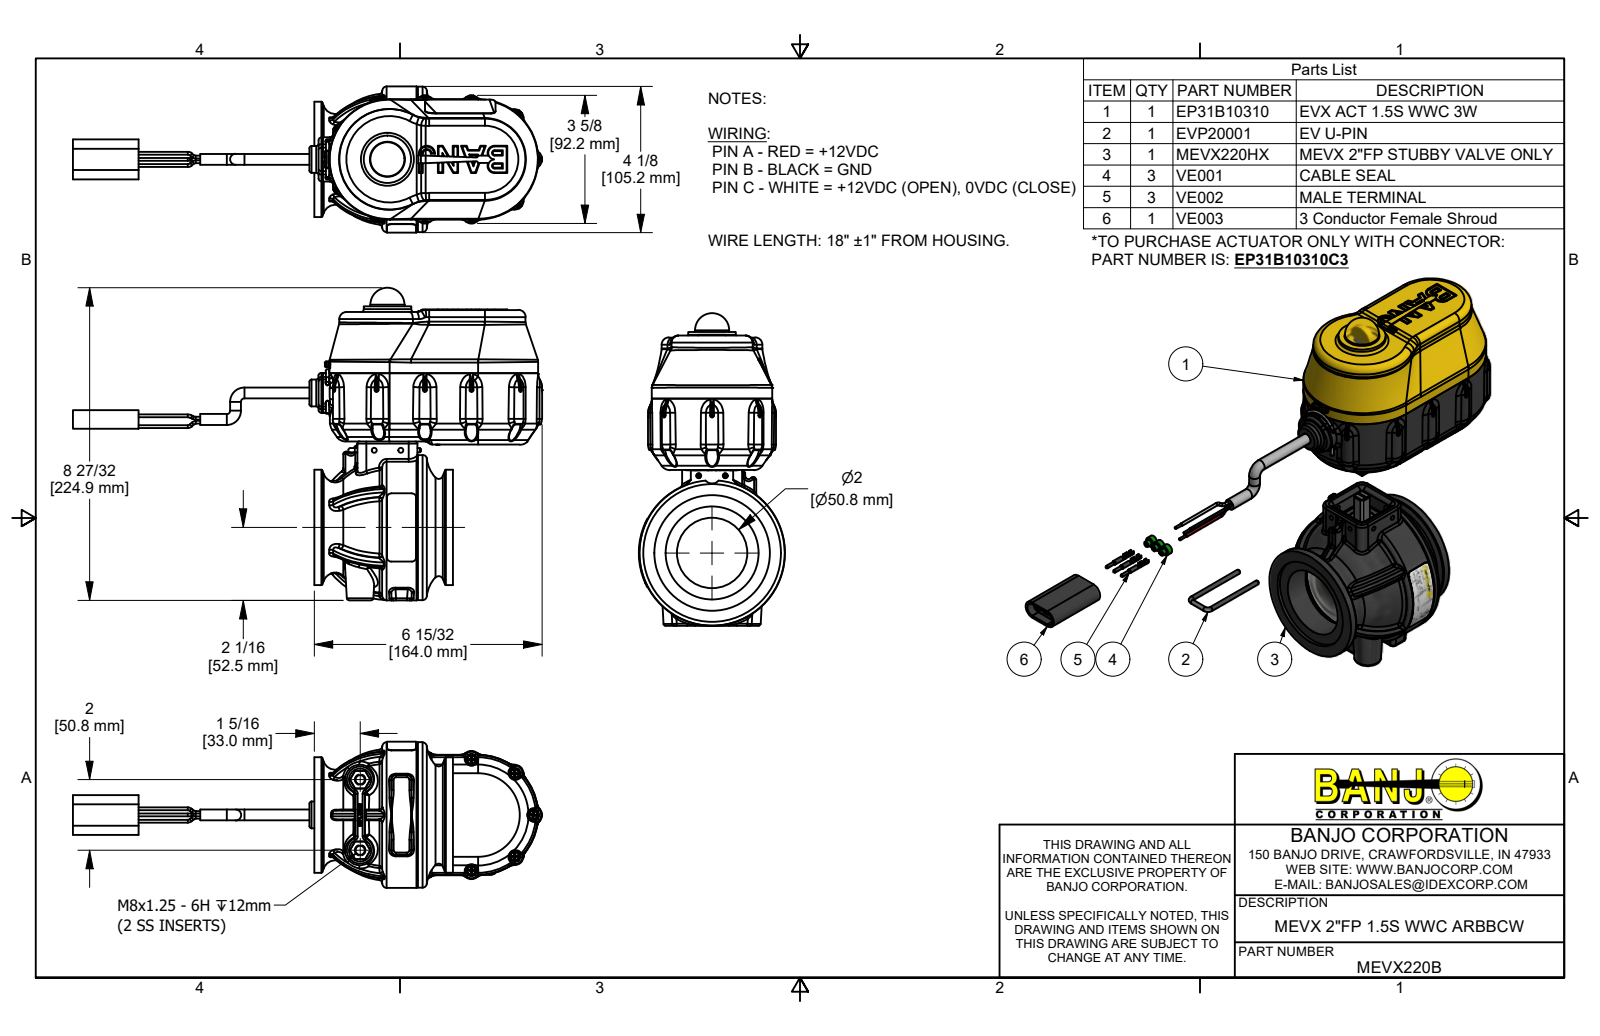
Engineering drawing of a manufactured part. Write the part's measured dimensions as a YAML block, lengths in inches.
part_name: "MEVX220B; EP31B10310; B61905PPHS; B632038PM (+8 more)"
step_written_by: "Autodesk Inventor 2019 (AUTOMOTIVE_DESIGN)"
units: inches
bodies: {solids: 91, faces: 10921, planar: 2893, cylindrical: 3118, other: 4910}
overall_size: [13.29, 8.856, 4.14]
volume: 53.88
surface_area: 619.3
round_holes:
  - {diameter: 0.095, count: 11}
  - {diameter: 0.15, count: 11}
  - {diameter: 0.08, count: 7}
  - {diameter: 0.15, count: 7}
  - {diameter: 0.135, count: 5}
  - {diameter: 0.107, count: 4}
  - {diameter: 0.126, count: 4}
  - {diameter: 0.136, count: 4}
  - {diameter: 0.148, count: 4}
  - {diameter: 0.17, count: 4}
  - {diameter: 0.25, count: 4}
  - {diameter: 0.049, count: 3}
round_bosses_or_shafts:
  - {diameter: 0.08, count: 18}
  - {diameter: 0.25, count: 17}
  - {diameter: 0.14, count: 11}
  - {diameter: 0.108, count: 11}
  - {diameter: 0.085, count: 11}
  - {diameter: 0.058, count: 6}
  - {diameter: 0.27, count: 4}
  - {diameter: 0.219, count: 4}
partial_cylinders:
  - {radius: 0.013, count: 180}
  - {radius: 0.04, count: 145}
  - {radius: 0.01, count: 84}
  - {radius: 0.02, count: 71}
  - {radius: 0.005, count: 55}
  - {radius: 0.03, count: 34}
  - {radius: 0.06, count: 31}
  - {radius: 0.08, count: 28}
face_to_face_distances: [0.1, 2.565, 0.06, 0.211, 0.151, 1.896, 1.836, 1.685, 0.569, 0.629]
hole_center_spacings: [2.22, 1.283, 2.69, 2.715, 0.75, 1.662, 1.774, 2.73]
